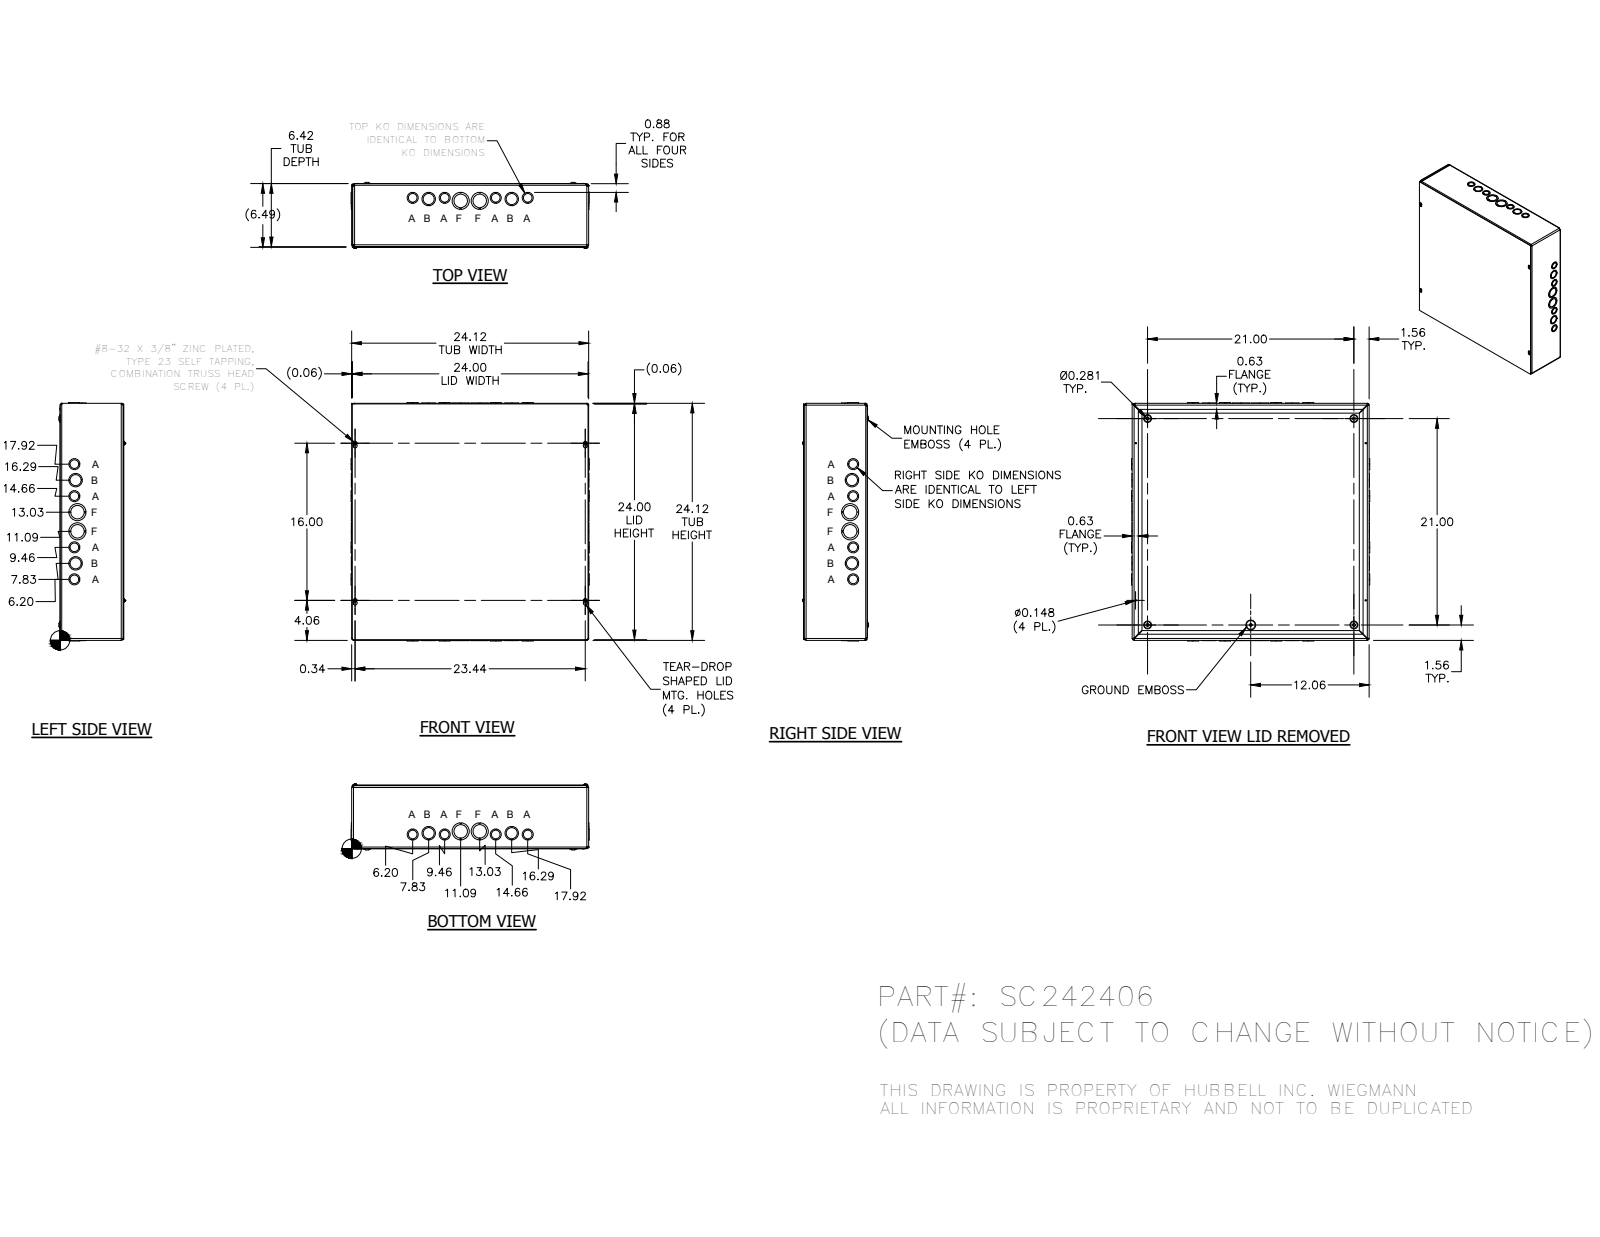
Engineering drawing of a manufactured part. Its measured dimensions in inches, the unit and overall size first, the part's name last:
Units: inches
Overall size (bounding box): 24.249 × 24.249 × 6.716
Round holes (diameter × count): ⌀1.125 ×12, ⌀0.875 ×8, ⌀1.375 ×8, ⌀0.148 ×4, ⌀0.3 ×4, ⌀1.75 ×4, ⌀0.165 ×1
Round bosses / shafts (diameter × count): ⌀0.18 ×8, ⌀0.384 ×4, ⌀0.164 ×4, ⌀0.228 ×1
Partial cylindrical surfaces — rounded edges, fillets, slot ends (radius × count): R0.125 ×12, R0.187 ×8, R0.055 ×4, R0.062 ×4, R0.094 ×4, R0.117 ×4, R0.124 ×4, R0.156 ×4
Main face-to-face distances: 0.074, 6.417, 0.062, 6.343, 24.063, 6.491, 24.125, 24.001, 0.062, 0.136
Hole centre spacings: 1.635, 1.659, 3.265, 3.584, 5.204, 6.831, 8.46, 18.54
Bodies: 38 solids, 1255 faces (838 planar, 267 cylindrical, 150 other)
Part name (STEP PRODUCT): SC2424BKP; SC242406WRA; SC2424LID; 34056 (+1 more)
STEP written by: Autodesk Inventor 2014 (AUTOMOTIVE_DESIGN)
